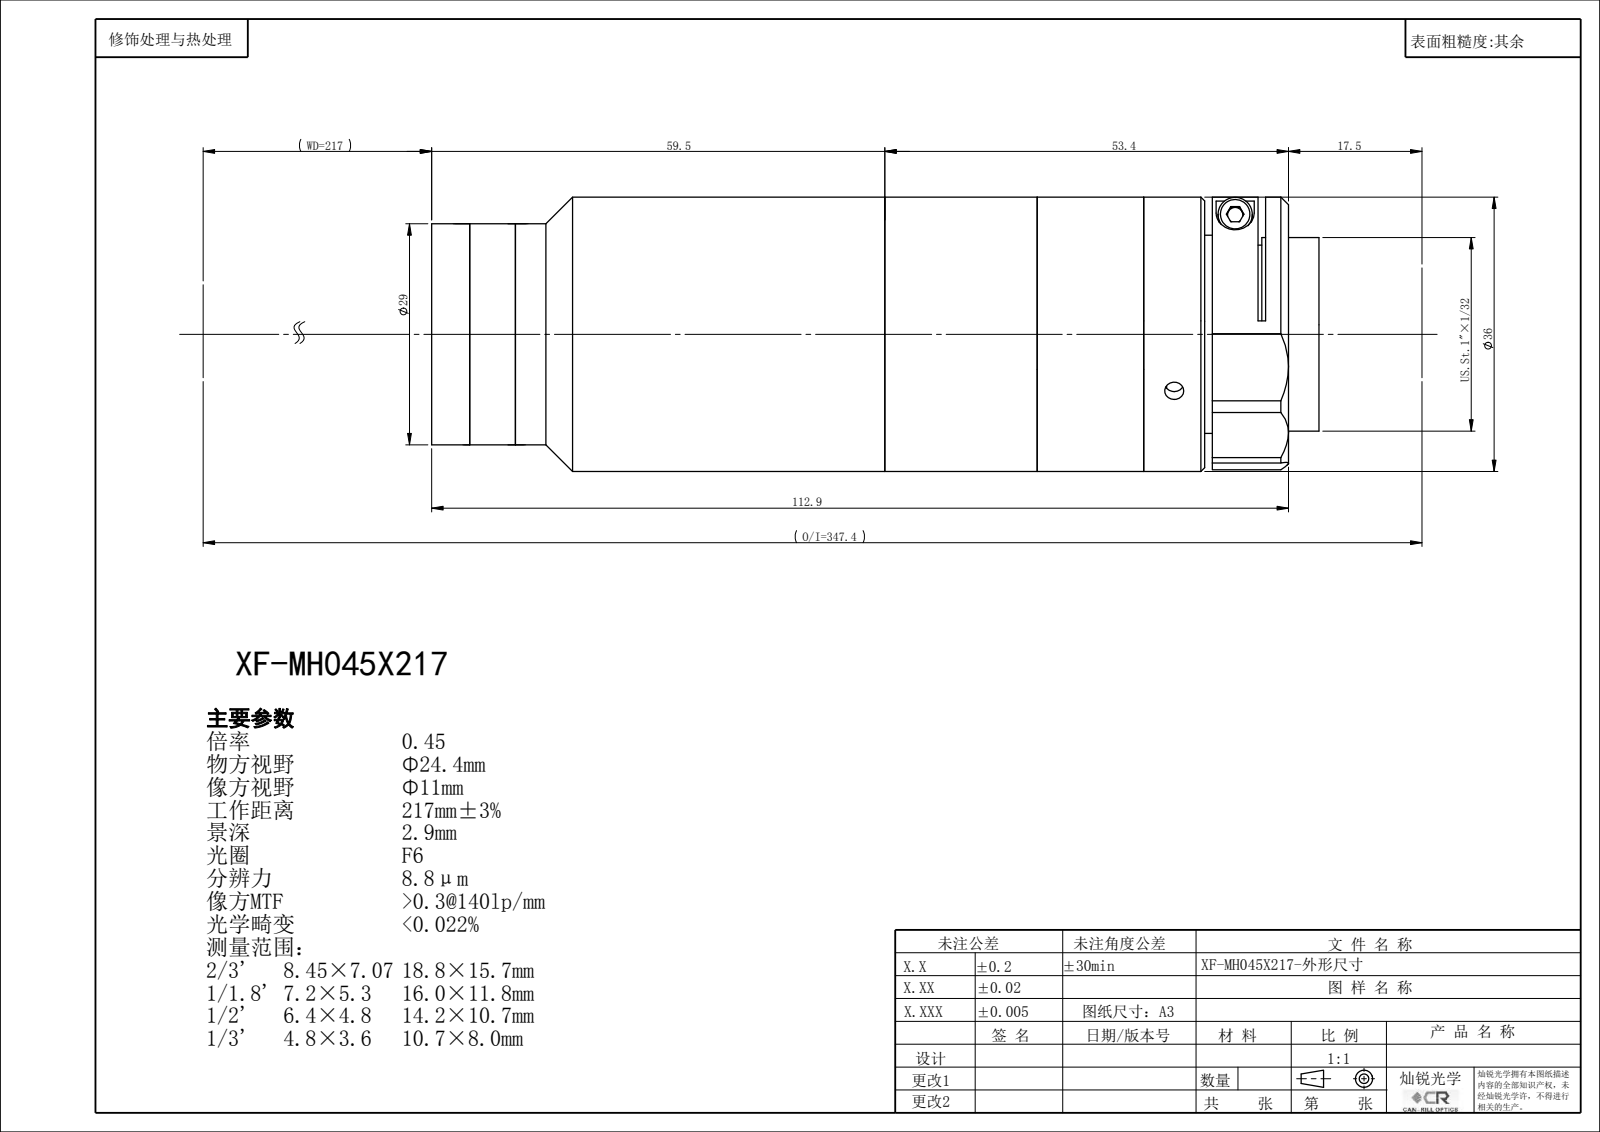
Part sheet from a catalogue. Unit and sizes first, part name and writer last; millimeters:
Units: millimetres
Overall size (bounding box): 116.93 × 36 × 36
Round holes (diameter × count): ⌀2.5 ×3, ⌀18 ×1, ⌀22.4 ×1, ⌀24 ×1, ⌀24.9 ×1, ⌀26.4 ×1
Round bosses / shafts (diameter × count): ⌀36 ×1, ⌀34 ×1, ⌀29 ×1, ⌀25.4 ×1
Main face-to-face distances: 19.43, 1.5, 17.93, 14, 31.93, 33.43, 20, 34, 51.93, 53.43
Bodies: 0 solids, 127 faces (63 planar, 42 cylindrical, 22 other)
Part name (STEP PRODUCT): XF-MH045X217
STEP written by: SolidWorks 2022 (CONFIG_CONTROL_DESIGN)
